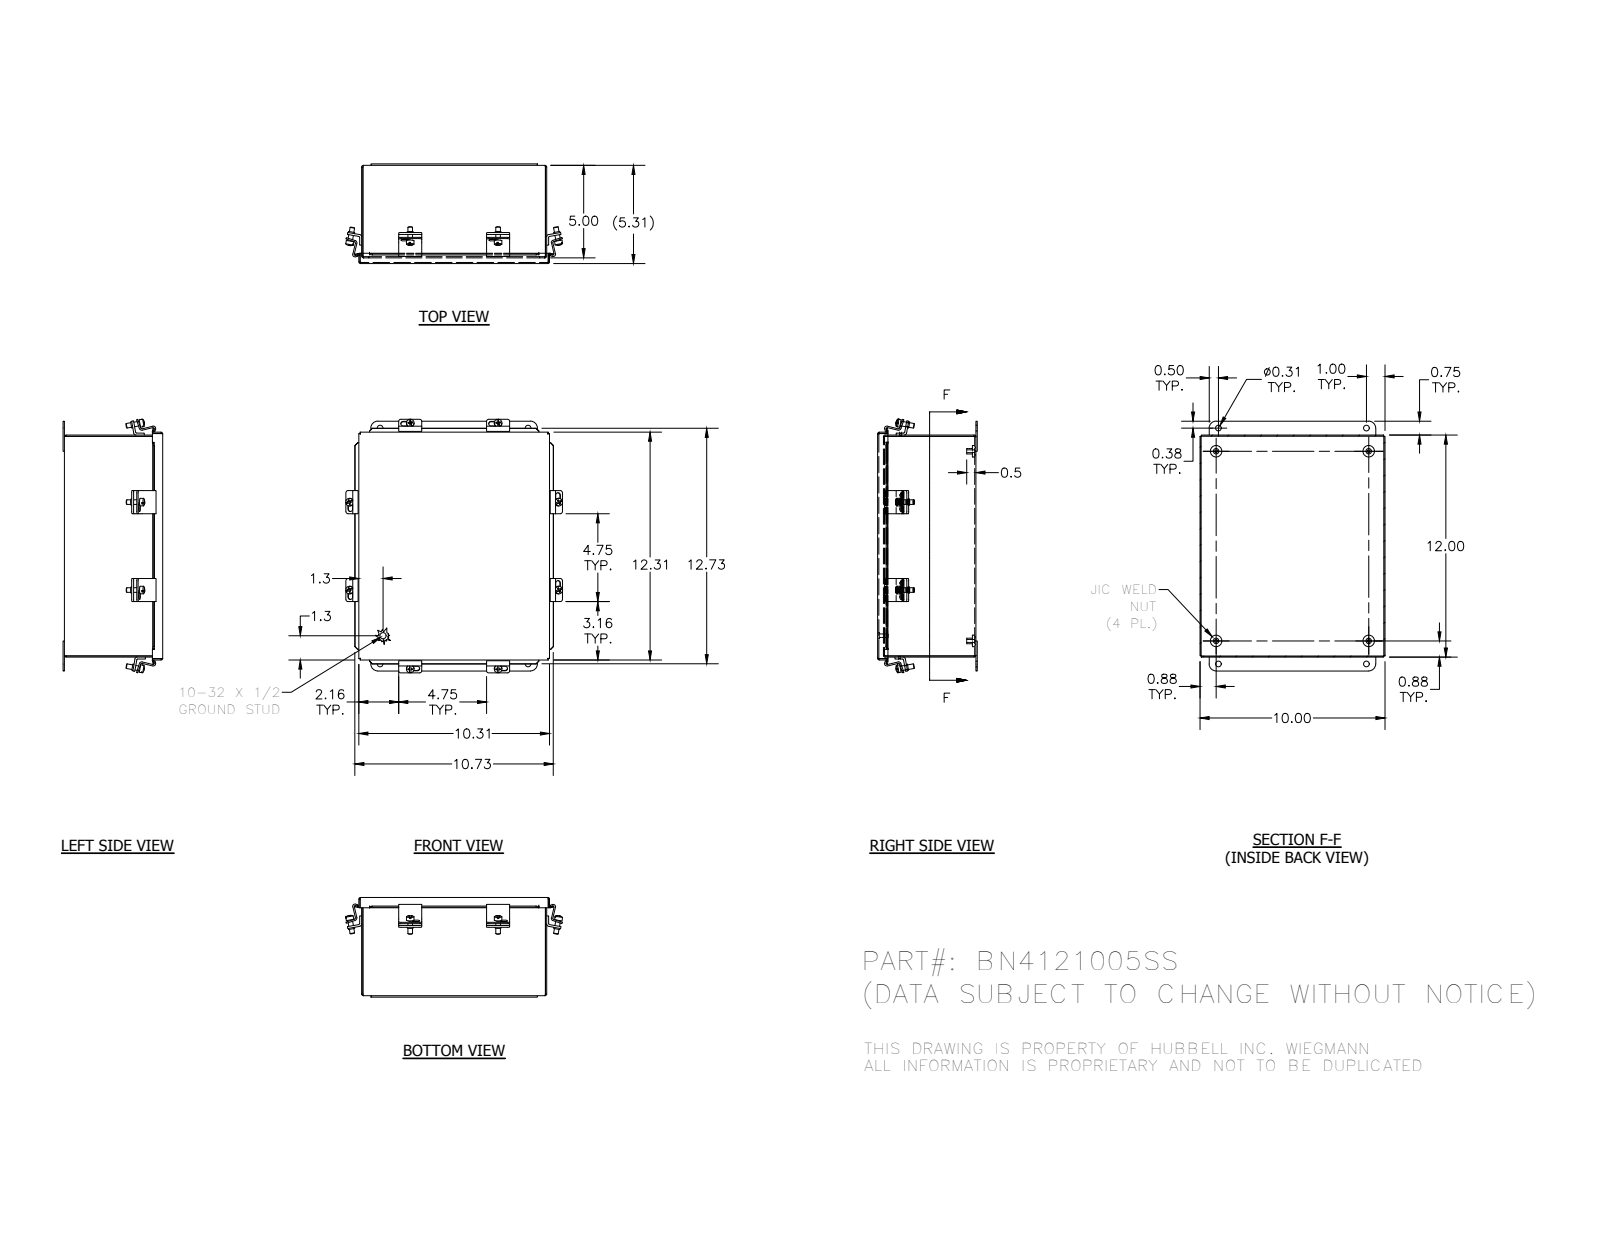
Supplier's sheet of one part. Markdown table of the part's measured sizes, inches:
| quantity | value |
| --- | --- |
| part name | 34973_1; C2002_1; C2001_1; 372135_1 (+5 more) |
| STEP written by | SolidWorks 2014 (AUTOMOTIVE_DESIGN) |
| units | inches |
| bodies | 33 solids, 917 faces (439 planar, 328 cylindrical, 150 other) |
| overall size | 13.712 × 11.724 × 5.388 |
| volume | 36.53 in³ |
| surface area | 1 148 in² |
| round holes (diameter × count) | 0.11 × 12, 0.196 × 8, 0.156 × 4, 0.31 × 4 |
| round bosses / shafts (diameter × count) | 0.41 × 8, 0.344 × 8, 0.25 × 8, 0.625 × 4, 0.3 × 4, 0.337 × 1, 0.19 × 1 |
| partial cylindrical surfaces (radius × count) | 0.125 × 32, 0.031 × 16, 0.094 × 16, 0.133 × 16, 0.063 × 12, 0.126 × 12, 0.375 × 4 |
| main face-to-face distances | 0.063, 5.25, 5.313, 5.187, 9.937, 11.937, 10, 9.875, 12, 11.875 |
| hole center spacings | 4.75, 0.75, 0.063, 0.753, 1.256, 4.75, 11.501, 14.081 |
